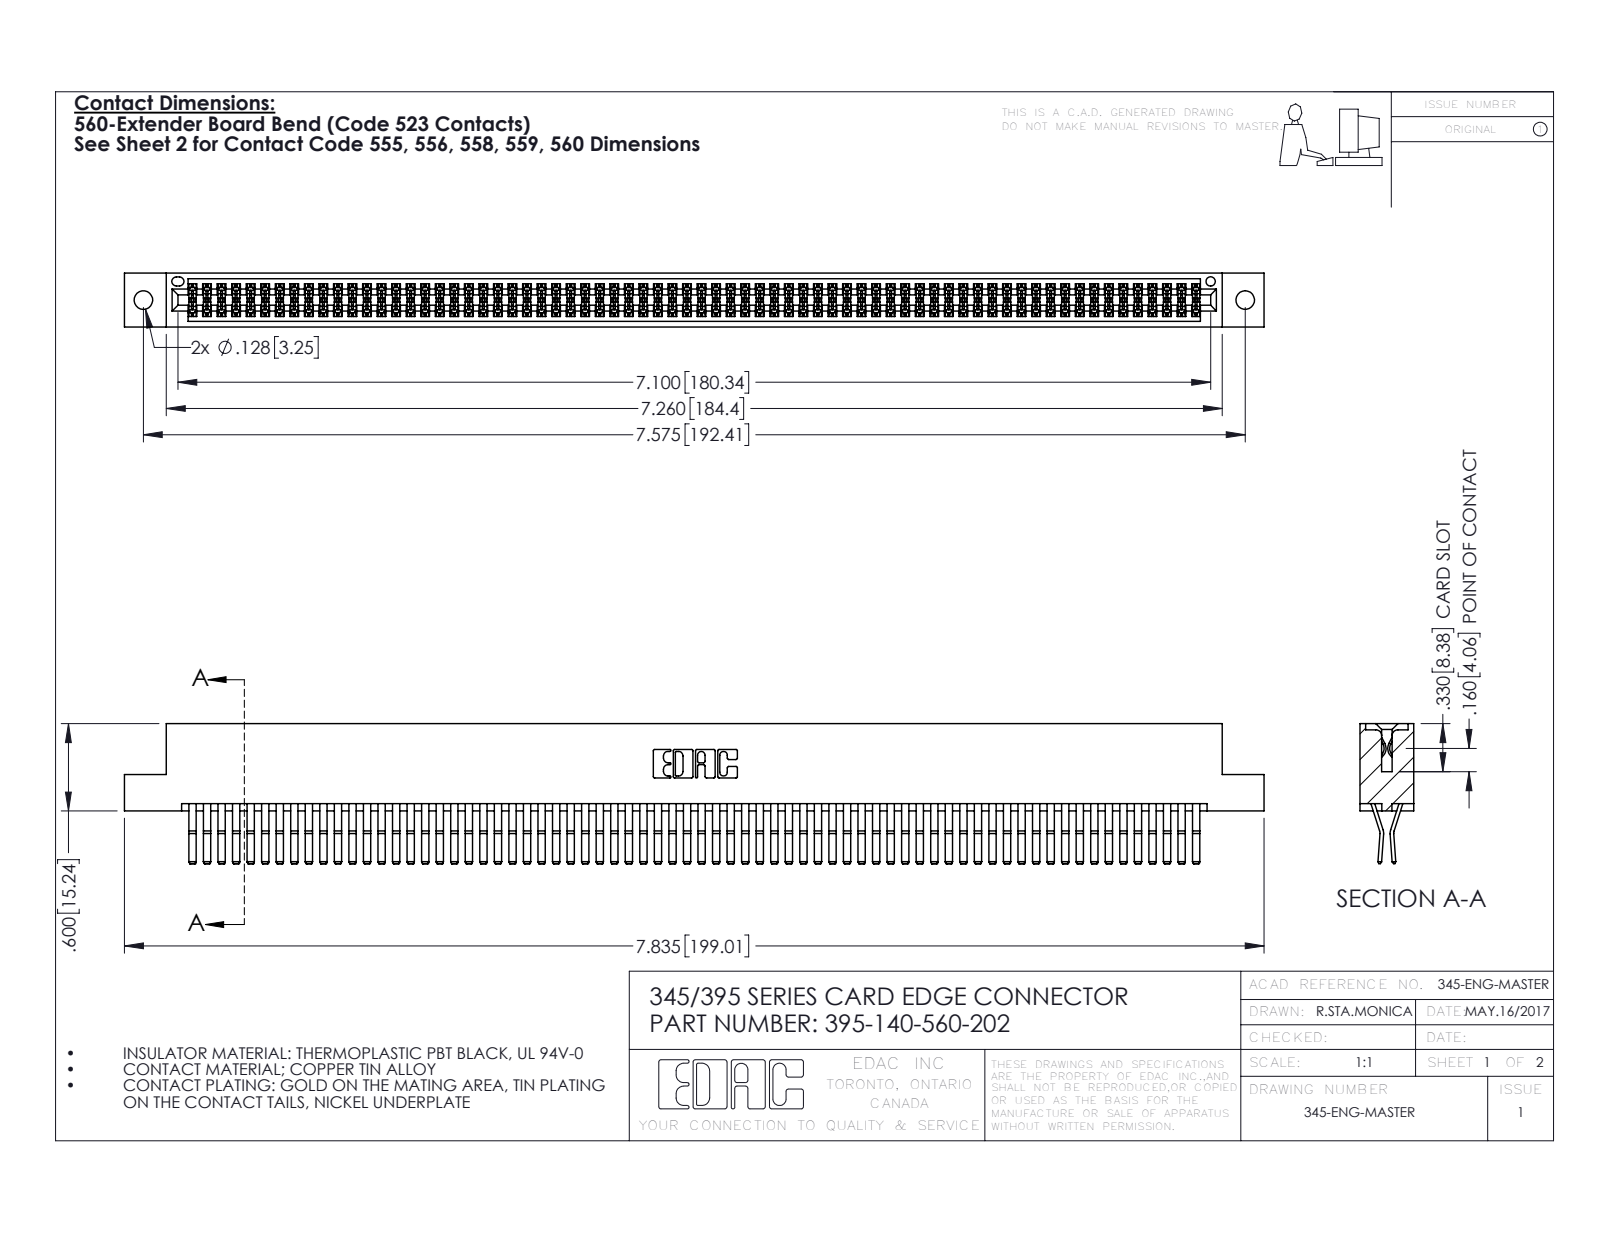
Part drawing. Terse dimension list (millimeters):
name: 345 Part_Flush Mounting Lugs - 0.128 Dia; 345-292-001_560 Tail; 395-140-560-202
written by: SolidWorks 2016 (CONFIG_CONTROL_DESIGN)
unit: mm
bodies: 141 solids, 7406 faces (4700 planar, 2706 cylindrical, 0 other)
size: 199 × 24.4 × 9.4
volume: 20 470 mm³; area: 32 890 mm²
holes: 2× ⌀3.3, 1× ⌀1.6
rounds: 210× R0.2, 22× R0.3, 6× R0.2, 6× R0.8, 3× R0.7, 2× R0.3, 2× R0.4, 2× R0.5
face distances: 0.6, 7.6, 1.8, 5.1, 9.4, 2.5, 6.9, 5.7, 4.4, 3.8
hole spacings: 6.9, 186.4, 192.4
